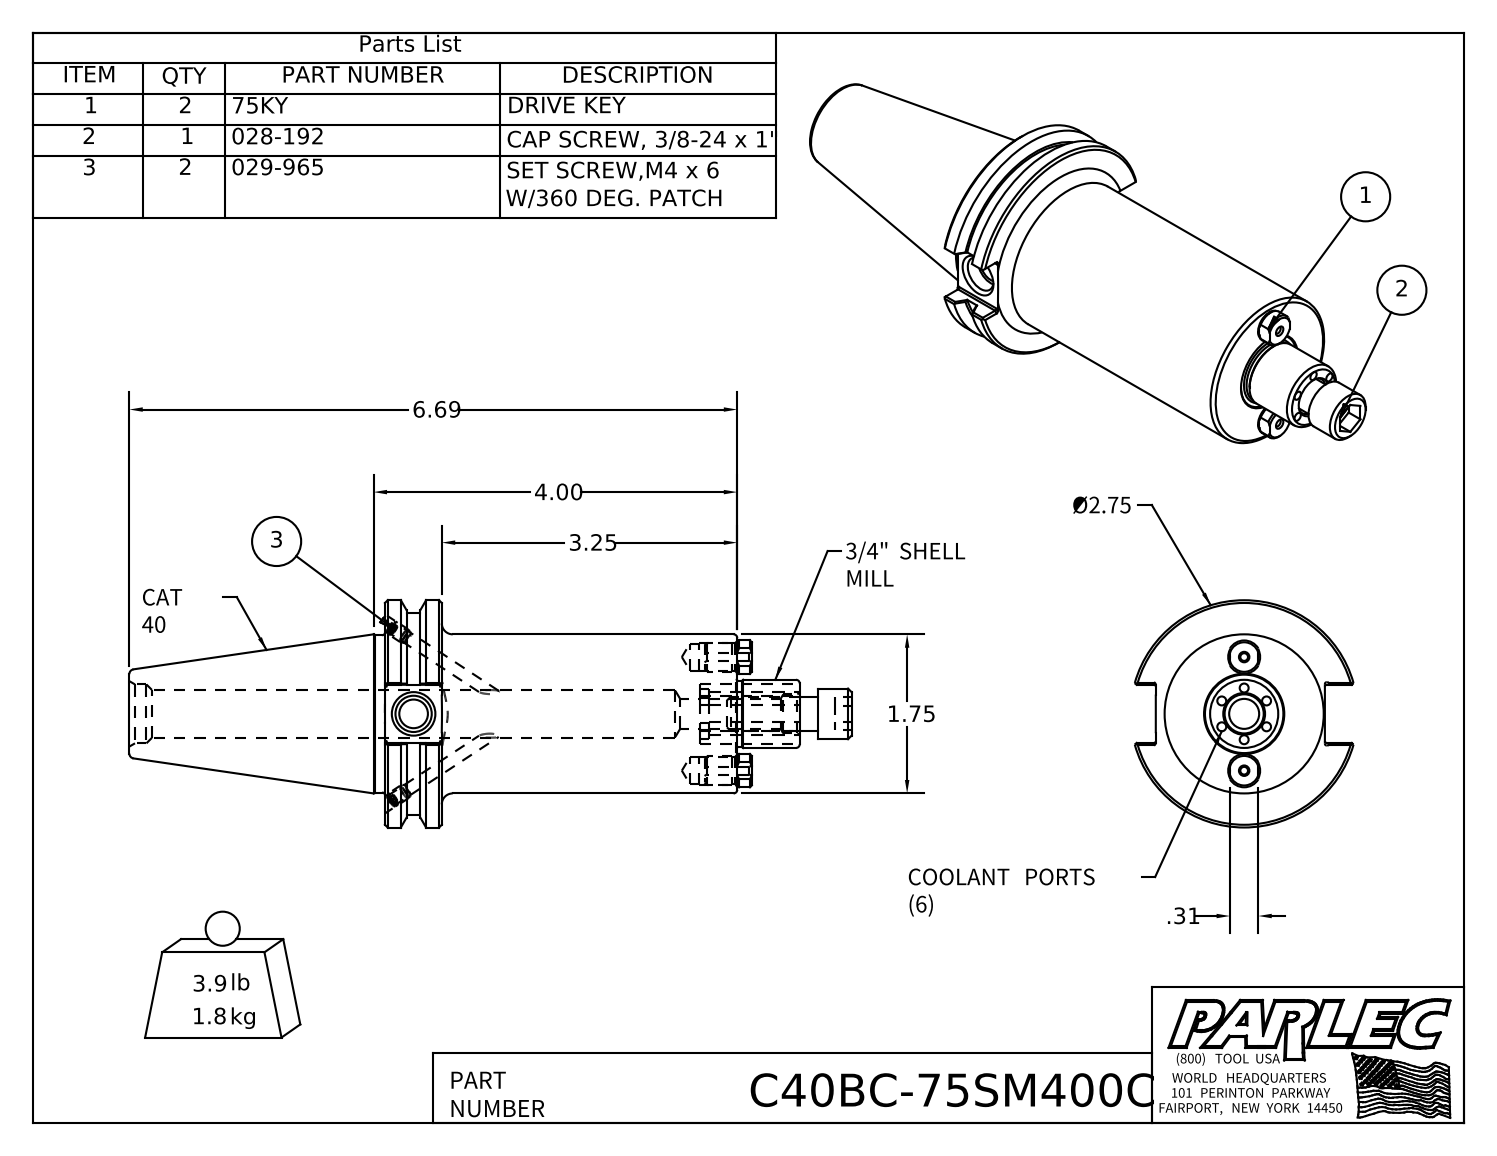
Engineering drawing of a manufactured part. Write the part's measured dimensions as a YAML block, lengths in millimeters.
part_name: "C40BC-75SM400C-1; 75KY; 028-192; 029-965 (+4 more)"
step_written_by: "Autodesk Inventor 2016 (AUTOMOTIVE_DESIGN)"
units: millimeters
bodies: {solids: 6, faces: 208, planar: 82, cylindrical: 67, other: 59}
overall_size: [201.83, 63.5, 61.11]
volume: 223673
surface_area: 42007
round_holes:
  - {diameter: 2.5, count: 6}
  - {diameter: 2.15, count: 2}
  - {diameter: 3.3, count: 2}
  - {diameter: 4.1, count: 2}
  - {diameter: 7.54, count: 2}
  - {diameter: 7.92, count: 2}
  - {diameter: 8, count: 1}
  - {diameter: 8.38, count: 1}
  - {diameter: 10.13, count: 1}
  - {diameter: 10.92, count: 1}
  - {diameter: 13.39, count: 1}
  - {diameter: 16.46, count: 1}
round_bosses_or_shafts:
  - {diameter: 8.08, count: 2}
  - {diameter: 7.62, count: 2}
  - {diameter: 4.2, count: 2}
  - {diameter: 4, count: 2}
  - {diameter: 63.5, count: 1}
  - {diameter: 56.36, count: 1}
  - {diameter: 44.45, count: 1}
  - {diameter: 43.94, count: 1}
partial_cylinders:
  - {radius: 0.51, count: 12}
  - {radius: 4.63, count: 2}
  - {radius: 7.11, count: 1}
face_to_face_distances: [98.43, 15.88, 82.55, 16.26, 25.4, 5.08, 47.25, 71.42, 87.3, 169.85]
hole_center_spacings: [7.23, 12.52, 13.77, 20.47, 7.22, 8.65, 14.45, 15.88]
